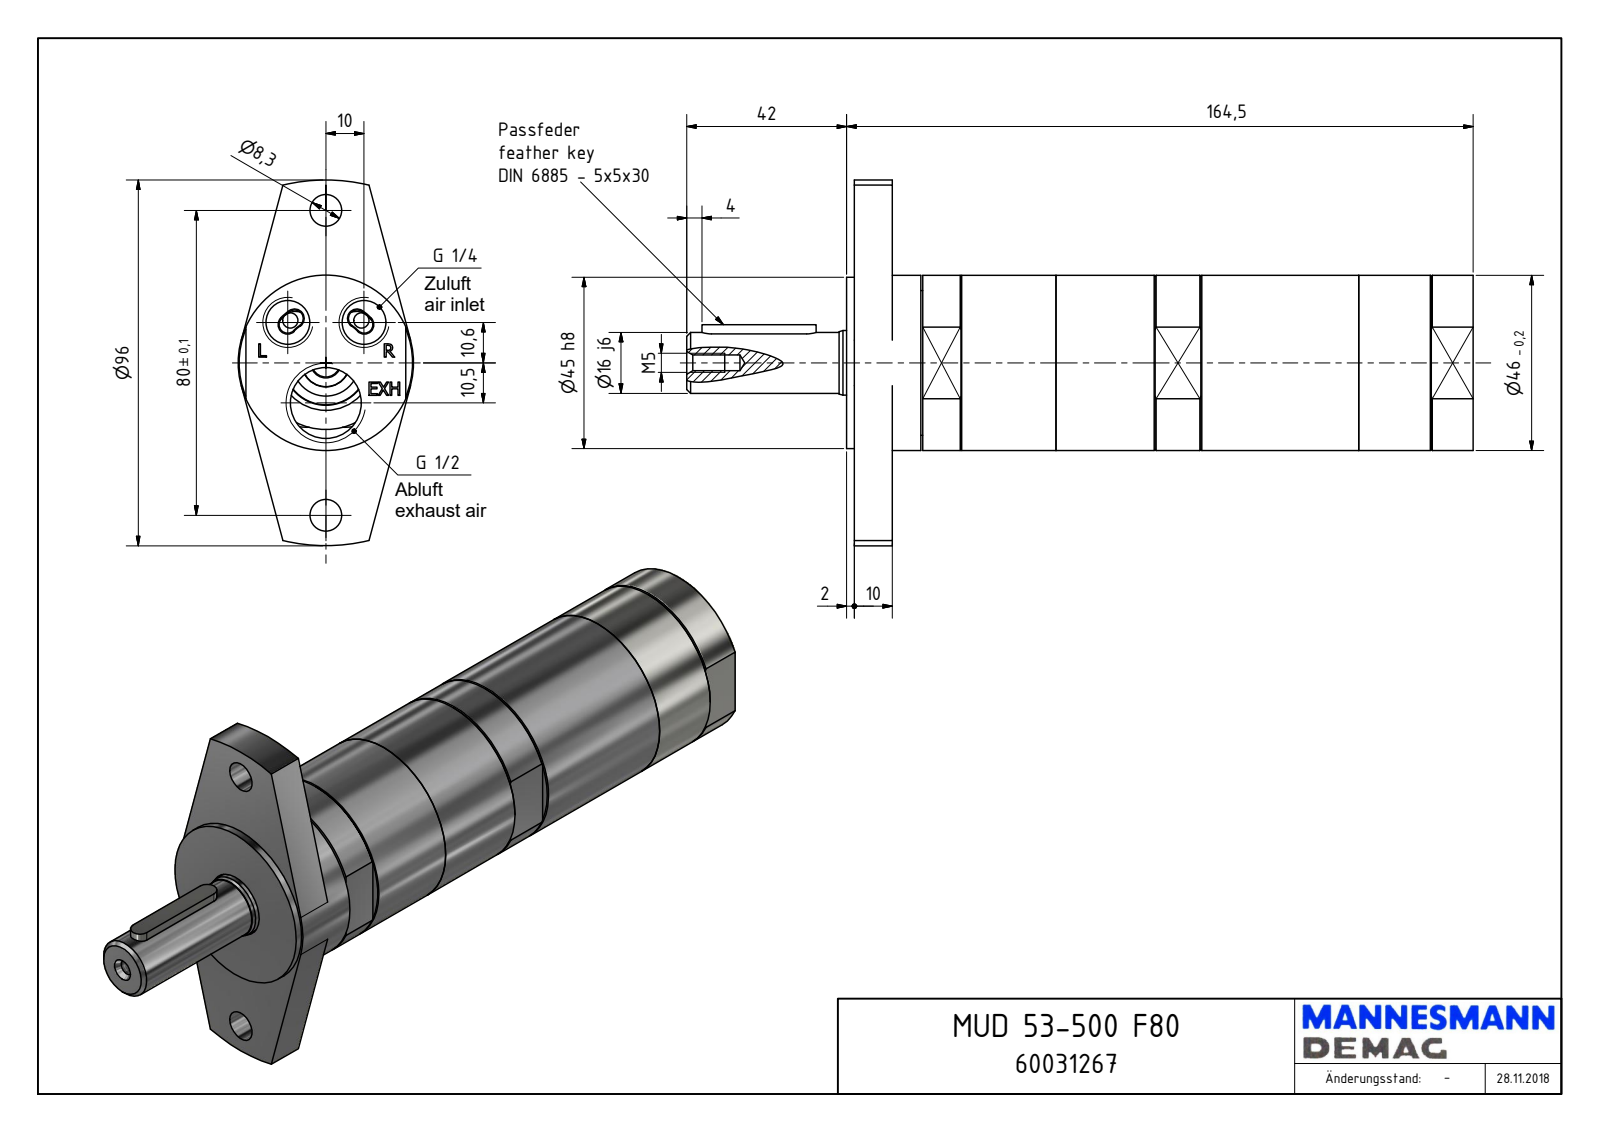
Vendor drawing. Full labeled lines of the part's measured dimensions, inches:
Part name (STEP PRODUCT): MUD 53-500 F80_60031267
STEP written by: Autodesk Inventor 2018 (AUTOMOTIVE_DESIGN)
Units: inches
Bodies: 1 solid, 177 faces (104 planar, 38 cylindrical, 35 other)
Overall size (bounding box): 8.13 × 3.78 × 1.811
Volume: 17.75 in³ · Surface area: 60.19 in²
Round holes (diameter × count): ⌀0.327 ×2, ⌀0.451 ×2, ⌀0.163 ×1, ⌀0.689 ×1, ⌀0.733 ×1, ⌀0.846 ×1, ⌀0.906 ×1, ⌀1.496 ×1, ⌀1.511 ×1
Round bosses / shafts (diameter × count): ⌀1.811 ×1, ⌀1.772 ×1, ⌀0.77 ×1, ⌀0.667 ×1, ⌀0.63 ×1
Partial cylindrical surfaces — rounded edges, fillets, slot ends (radius × count): R0.098 ×2, R0.197 ×2, R0.697 ×1, R1.89 ×1
Main face-to-face distances: 0.394, 0.472, 0.079, 6.476, 6.398, 6.004, 1.654, 0.315, 5.689, 0.709
Hole centre spacings: 0.574, 0.919, 1.222, 1.575, 2.031, 0.413, 0.787, 1.161
